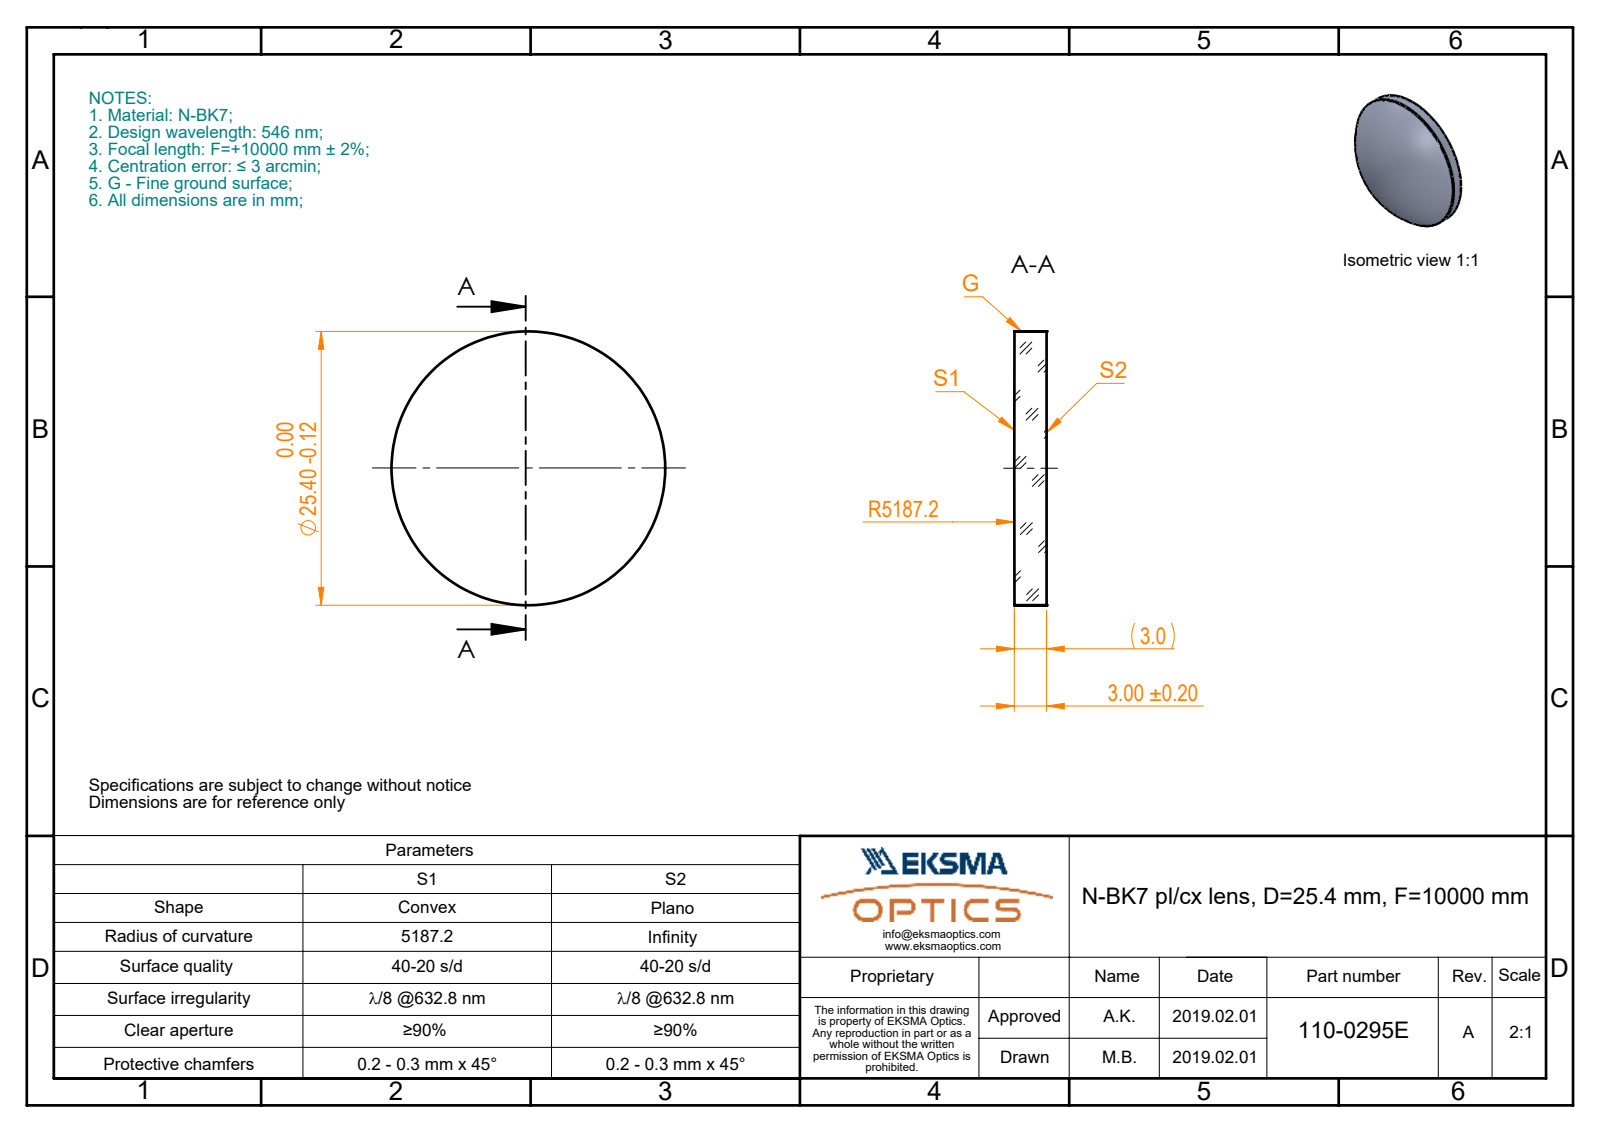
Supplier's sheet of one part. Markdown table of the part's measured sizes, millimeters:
| quantity | value |
| --- | --- |
| part name | 110-0295E BK7 pl-cx 25.4 F10000 |
| STEP written by | SolidWorks 2017 (CONFIG_CONTROL_DESIGN) |
| units | millimeters |
| bodies | 1 solid, 5 faces (1 planar, 2 cylindrical, 2 other) |
| overall size | 25.4 × 25.4 × 3 |
| volume | 1 516 mm³ |
| surface area | 1 252 mm² |
| round bosses / shafts (diameter × count) | 25.4 × 1 |
